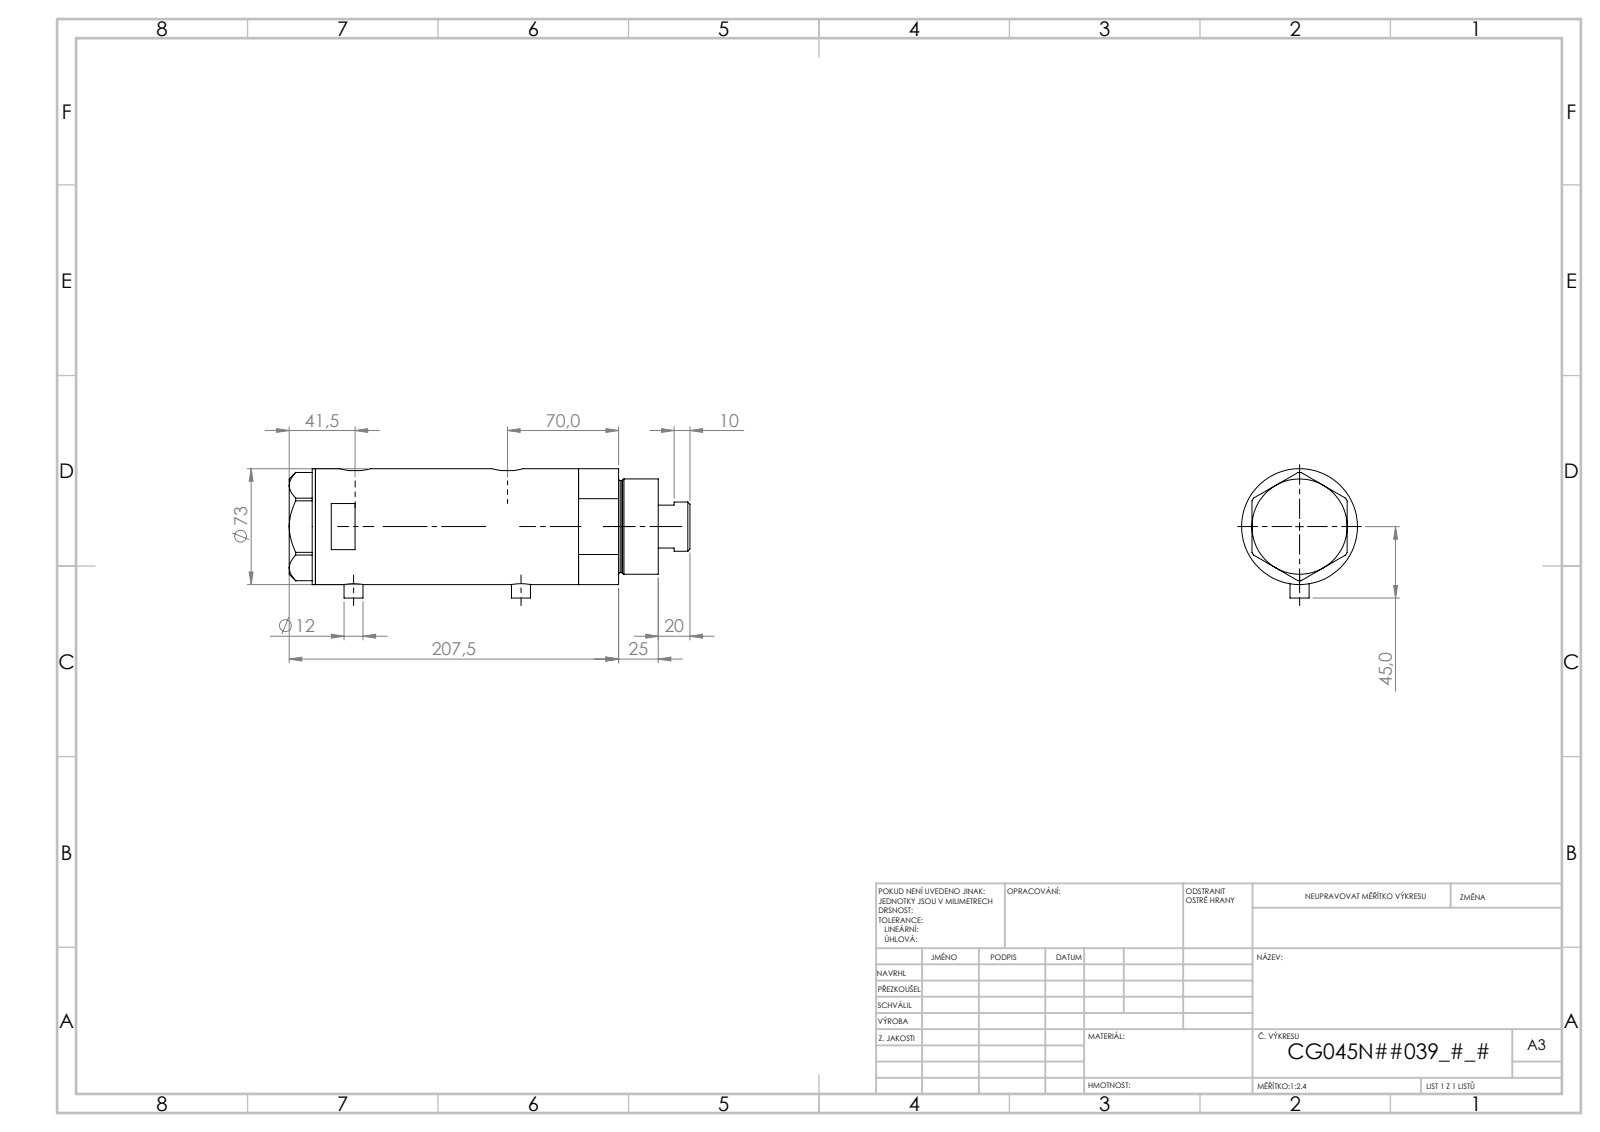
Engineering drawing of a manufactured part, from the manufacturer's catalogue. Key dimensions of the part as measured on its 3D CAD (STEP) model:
Part name (STEP PRODUCT): V270CG_VC; V270CG_BACK; V270CG_FRONT; V270CG_MIDDLE
STEP written by: SolidWorks 2019 (CONFIG_CONTROL_DESIGN)
Units: millimetres
Bodies: 4 solids, 125 faces (50 planar, 55 cylindrical, 20 other)
Overall size (bounding box): 230.52 × 74.1 × 73
Volume: 799 324 mm³ · Surface area: 138 319 mm²
Round holes (diameter × count): ⌀5 ×2, ⌀12.5 ×2, ⌀13.16 ×2, ⌀10.5 ×1, ⌀32 ×1, ⌀33.5 ×1, ⌀45 ×1, ⌀48 ×1, ⌀64 ×1
Round bosses / shafts (diameter × count): ⌀12 ×2, ⌀73 ×1, ⌀60 ×1, ⌀58 ×1, ⌀31 ×1
Partial cylindrical surfaces — rounded edges, fillets, slot ends (radius × count): R10 ×2
Main face-to-face distances: 106.15, 42.5, 122.65, 80.15, 16.5, 16.51, 26, 25.99, 106.14, 194.02
Hole centre spacings: 90.65, 0.99, 1, 8.5, 8.51, 81.15, 82.14, 82.15
